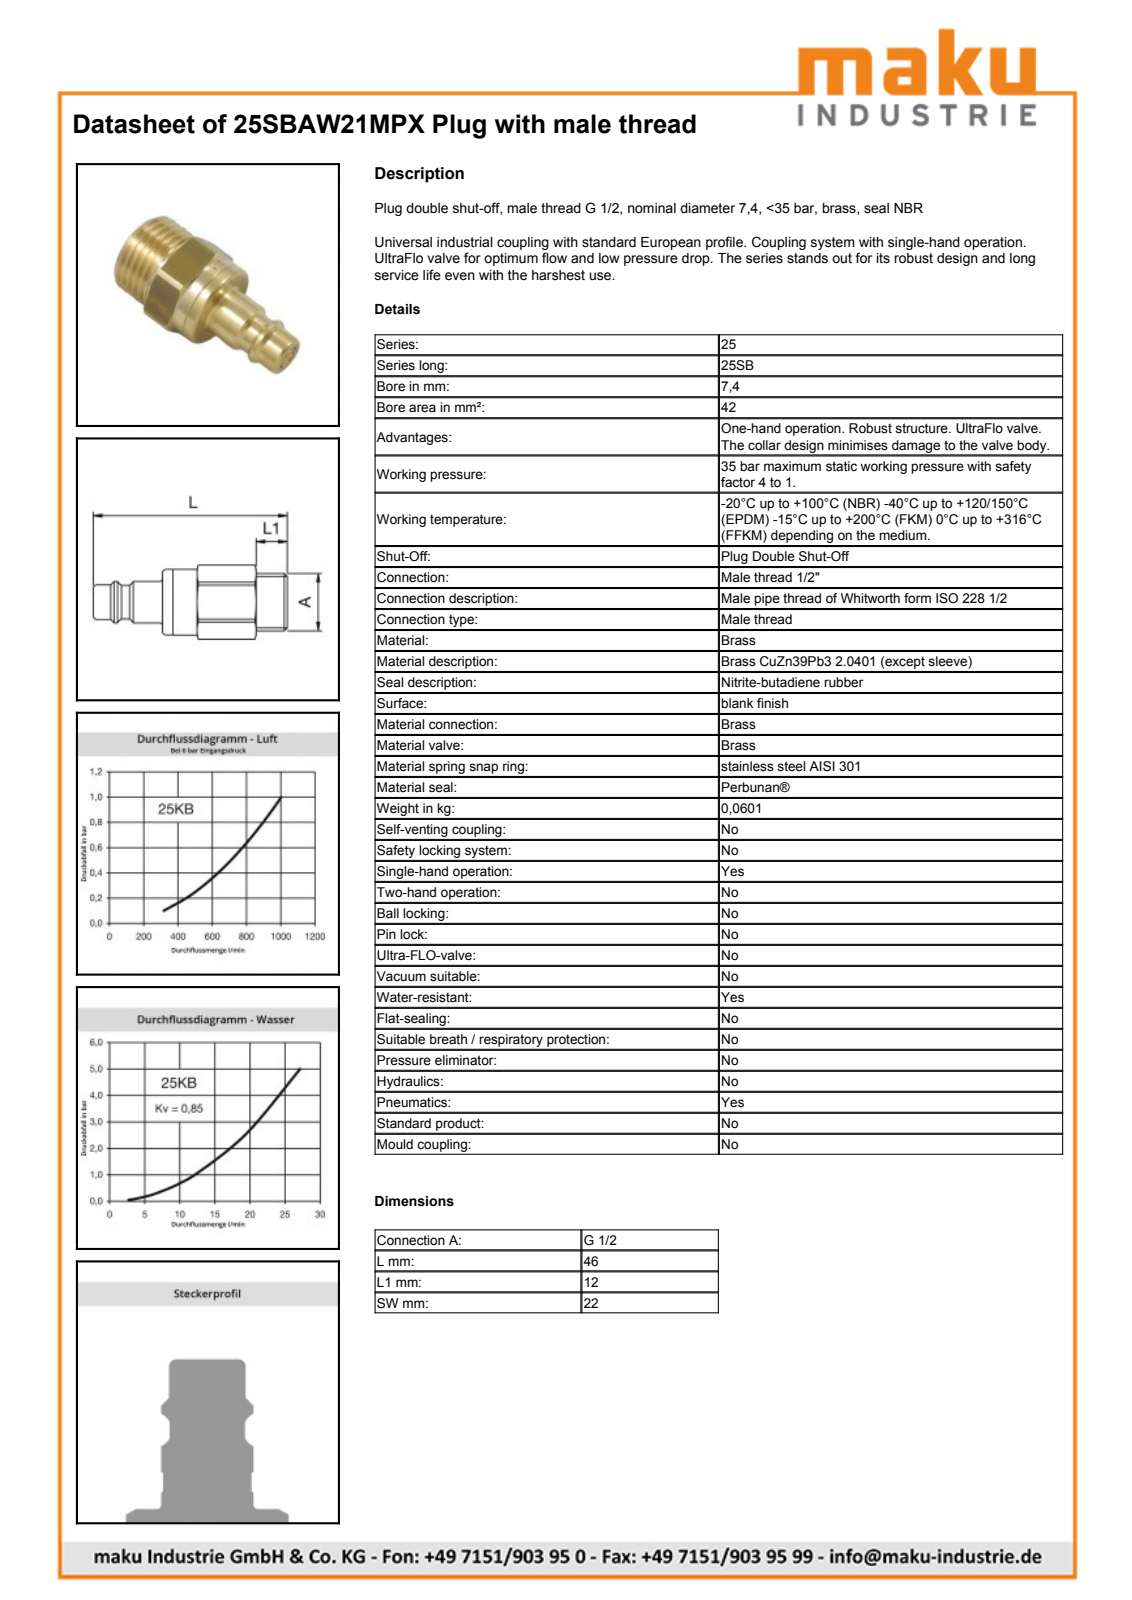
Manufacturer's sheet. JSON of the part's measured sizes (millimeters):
{"part_name": "D112790", "step_written_by": "Autodesk Inventor 2013 (AUTOMOTIVE_DESIGN)", "units": "millimeters", "bodies": {"solids": 1, "faces": 50, "planar": 14, "cylindrical": 16, "other": 20}, "overall_size": [46.1, 24.61, 23.6], "volume_mm3": 11409, "surface_area_mm2": 3718, "round_holes": [[17.15, 1]], "round_bosses_or_shafts": [[21, 1], [20.95, 1], [16.84, 1], [16.5, 1], [12, 1], [10, 1], [9.75, 1]], "partial_cylinders_radius": [[12.4, 1]], "face_to_face_distances": [22, 26.1, 21.98, 20, 46.1, 34.1, 14.1, 12, 6.1, 8]}
